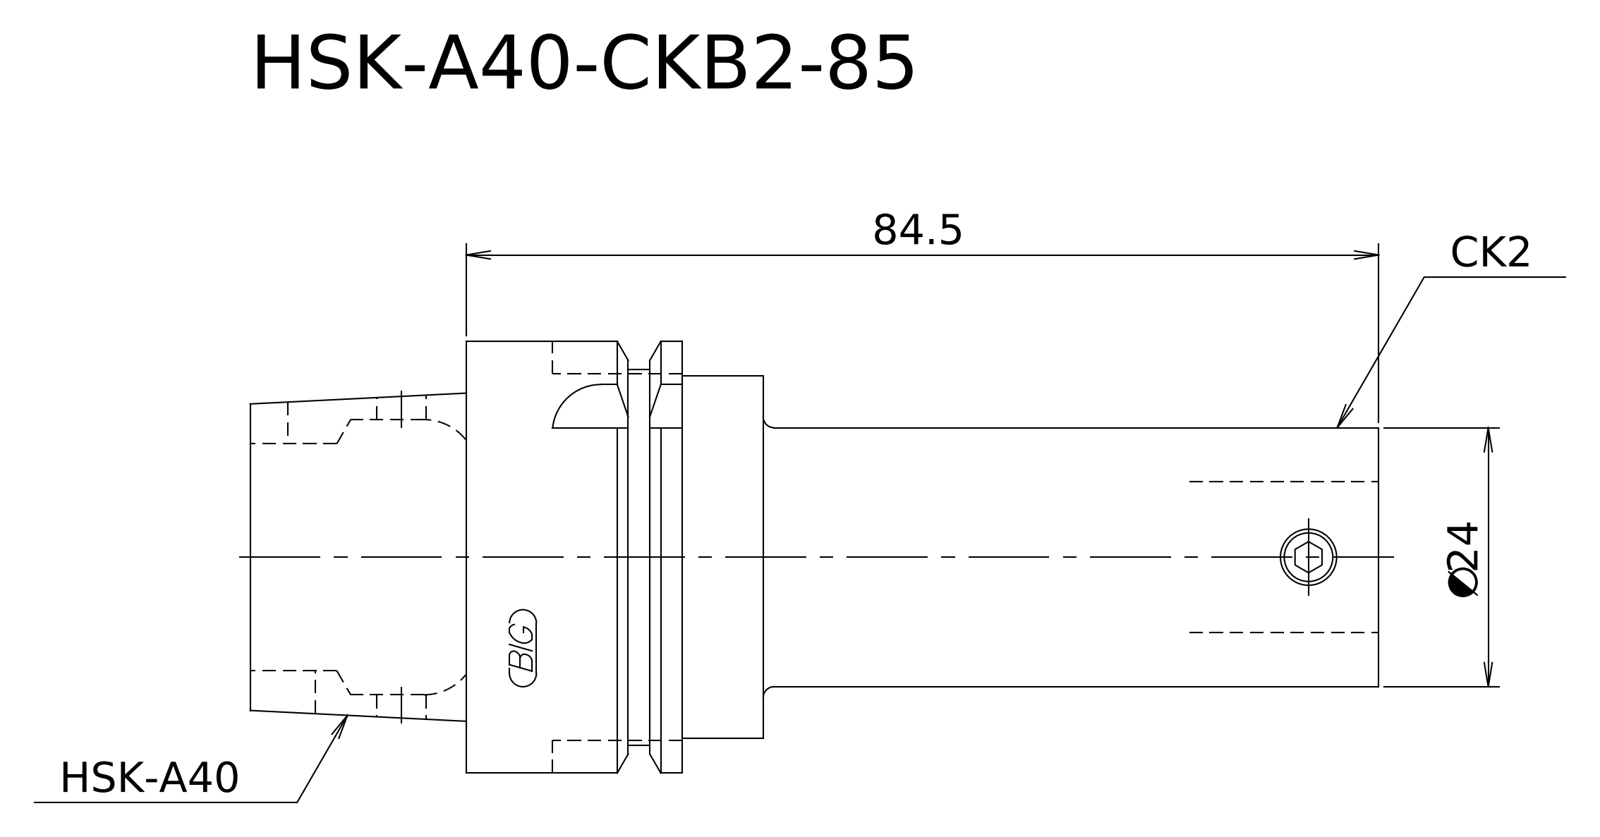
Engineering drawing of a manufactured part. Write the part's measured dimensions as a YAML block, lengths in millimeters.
step_written_by: "Kubotek KeyCreator V8.5.1 (14335) (CONFIG_CONTROL_DESIGN)"
units: millimeters
bodies: {solids: 1, faces: 17, planar: 7, cylindrical: 6, other: 4}
overall_size: [104.5, 40, 40]
volume: 70357
surface_area: 12223
round_bosses_or_shafts:
  - {diameter: 40, count: 1}
  - {diameter: 34.8, count: 1}
  - {diameter: 33.6, count: 1}
  - {diameter: 30.25, count: 1}
  - {diameter: 24, count: 1}
face_to_face_distances: [20, 84.5, 104.5, 64.5, 40, 57, 7.5, 27.5, 47.5, 67.5]
